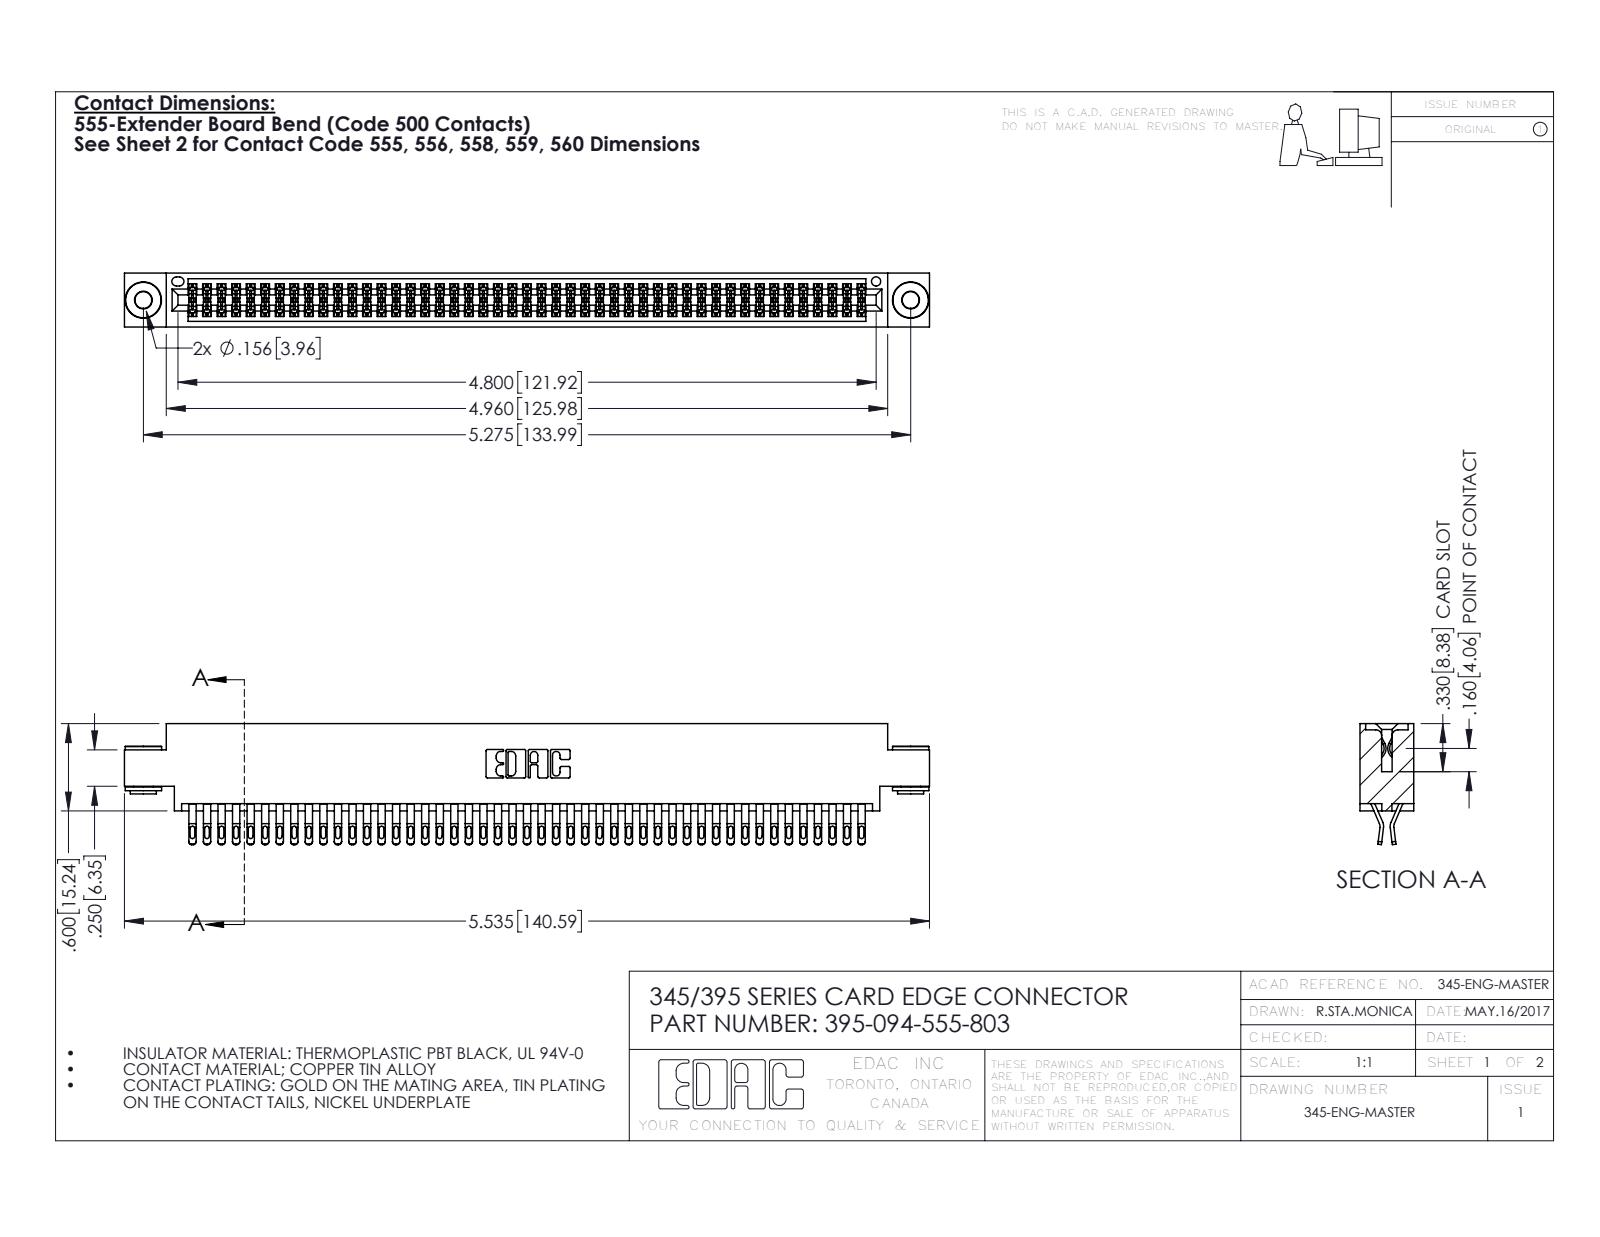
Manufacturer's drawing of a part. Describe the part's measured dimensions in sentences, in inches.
The part is named "395-094-555-803; 345 Part_0.170 Offset - 0.156 Dia-TH; 345-250-002_345-250-002-102; 345-292-001_555 Tail". Its 3-D file was written by "SolidWorks 2016 (CONFIG_CONTROL_DESIGN)". It is 97 solids with 5432 faces: 3008 planar, 2416 cylindrical and 8 other. Overall it measures 5.535 by 0.832 by 0.37 inches. Its volume is 0.847 cubic inches and its surface area 33.97 square inches. Round holes: 2 of diameter 0.116, 2 of diameter 0.156, 1 of diameter 0.064. Round bosses or shafts: 2 of diameter 0.25, 2 of diameter 0.18, 2 of diameter 0.136. Partial cylindrical surfaces (rounded edges, fillets, slot ends): 235 of radius 0.016, 188 of radius 0.02, 141 of radius 0.006, 22 of radius 0.01, 6 of radius 0.007, 6 of radius 0.031, 3 of radius 0.026, 2 of radius 0.01. The main face-to-face distances are 0.072, 0.298, 0.37, 0.025, 0.2, 0.098, 0.272, 0.225, 0.175, 0.149. The hole center spacings are 0.27, 5.039, 5.275.
